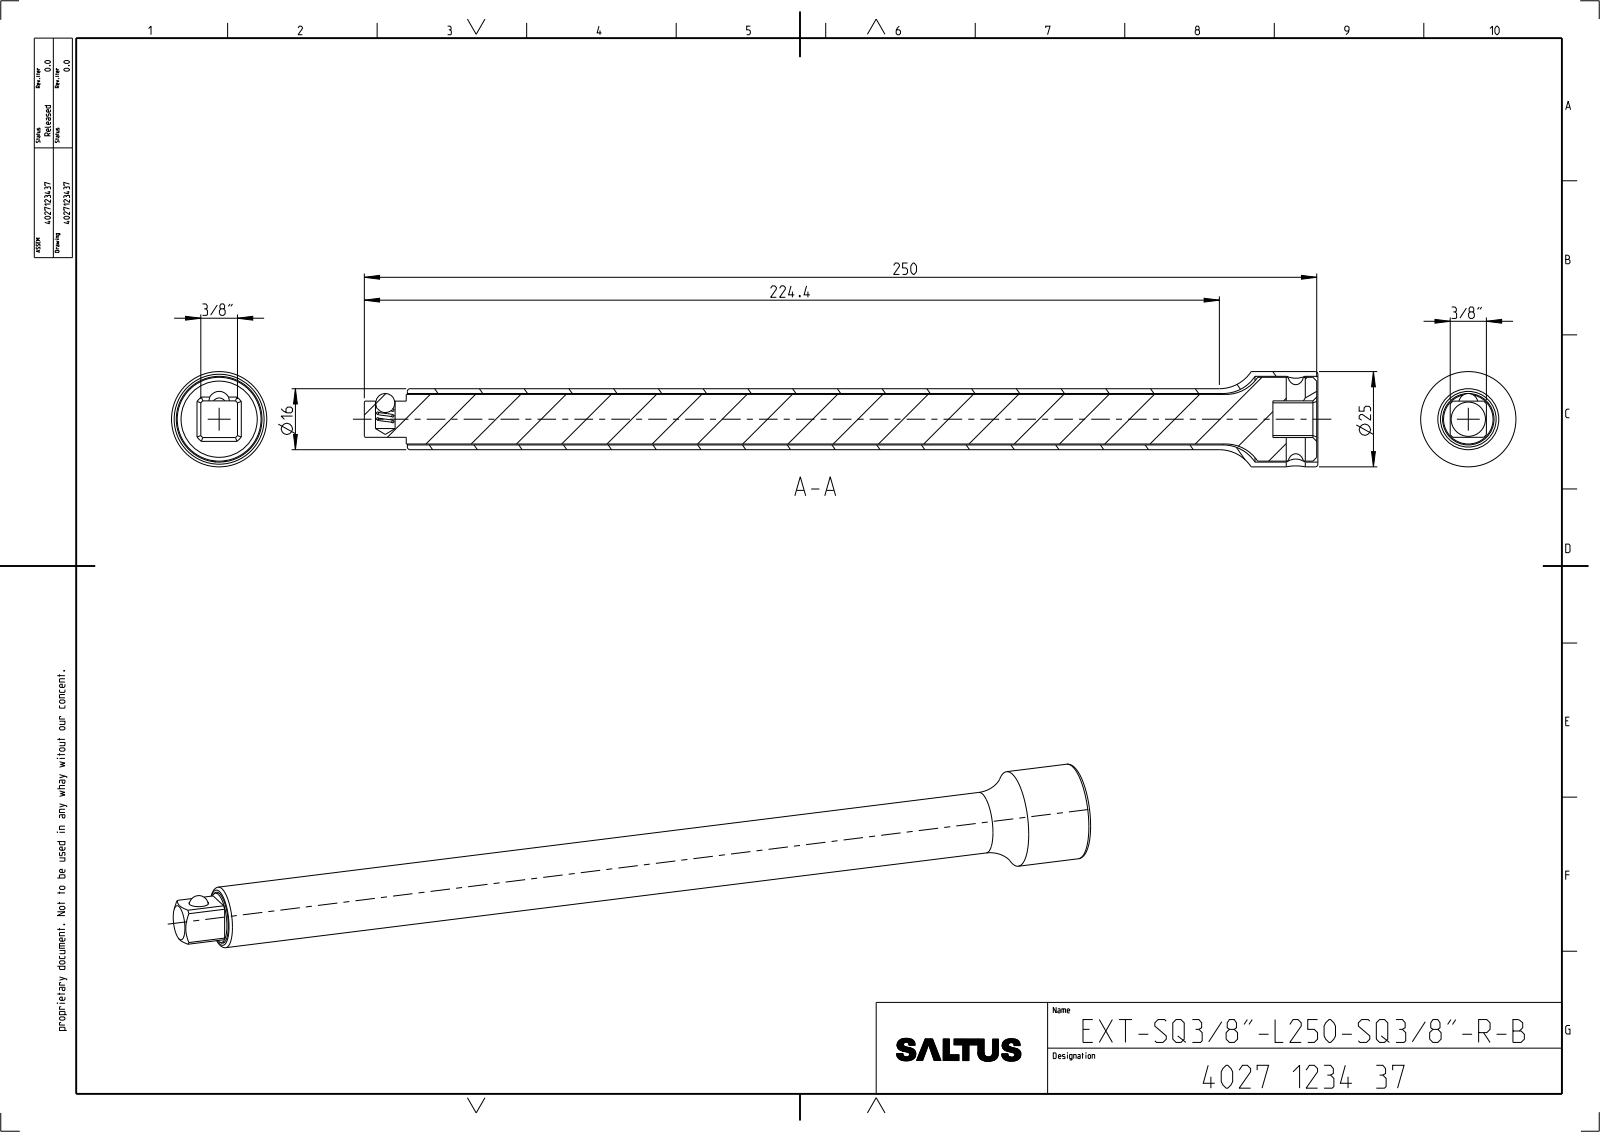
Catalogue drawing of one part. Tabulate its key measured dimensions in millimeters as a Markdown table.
| quantity | value |
| --- | --- |
| part name | 4027123447; 4027040475; 4027123437_ASM |
| STEP written by | CREO PARAMETRIC BY PTC INC, 2022414 (CONFIG_CONTROL_DESIGN) |
| units | millimeters |
| bodies | 3 solids, 80 faces (20 planar, 33 cylindrical, 27 other) |
| overall size | 250.3 × 25 × 25 |
| volume | 50 226 mm³ |
| surface area | 35 571 mm² |
| round holes (diameter × count) | 5 × 1, 5.15 × 1, 13.5 × 1, 22.5 × 1 |
| round bosses / shafts (diameter × count) | 25 × 1, 22 × 1, 16 × 1, 13 × 1 |
| partial cylindrical surfaces (radius × count) | 3 × 1, 6.22 × 1, 6.45 × 1 |
| main face-to-face distances | 9.56, 9.62, 9.5, 11.5, 239, 250, 238.5, 227.5, 11, 11.8 |
| hole center spacings | 239 |
